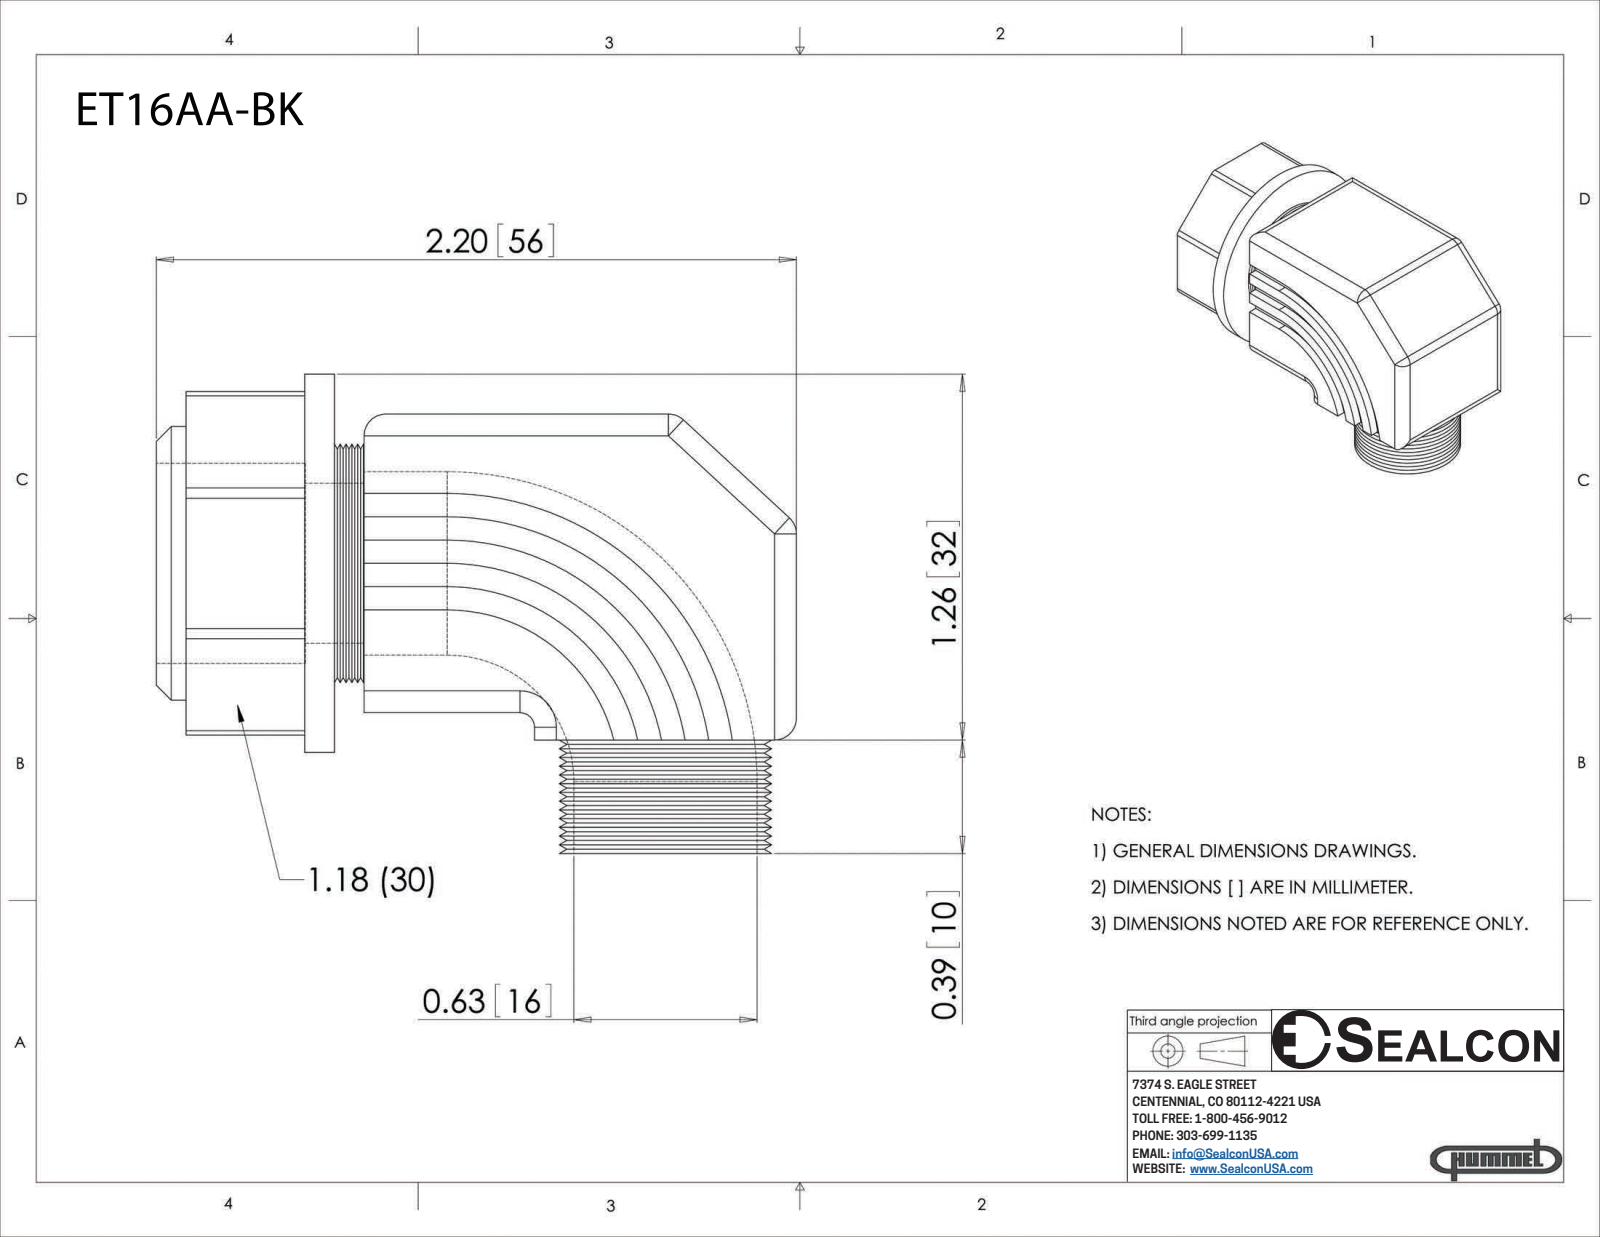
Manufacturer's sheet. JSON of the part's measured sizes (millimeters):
{"part_name": "ET16AA-BK", "step_written_by": "SolidWorks 2008 (CONFIG_CONTROL_DESIGN)", "units": "millimeters", "bodies": {"solids": 3, "faces": 211, "planar": 50, "cylindrical": 51, "other": 110}, "overall_size": [55.9, 41.8, 33], "volume_mm3": 26010, "surface_area_mm2": 12830, "round_holes": [[16, 2], [14, 1], [17.4, 1]], "round_bosses_or_shafts": [[33, 1], [23.9, 1], [20.8, 1]], "partial_cylinders_radius": [[1.9, 14], [1.3, 9], [15, 1], [17, 1], [19.1, 1], [21.1, 1], [23.1, 1], [25.1, 1]], "face_to_face_distances": [25.4, 1.5, 23.9, 13, 28.4, 40.3, 2.6, 37.7, 15.5, 53.3]}
